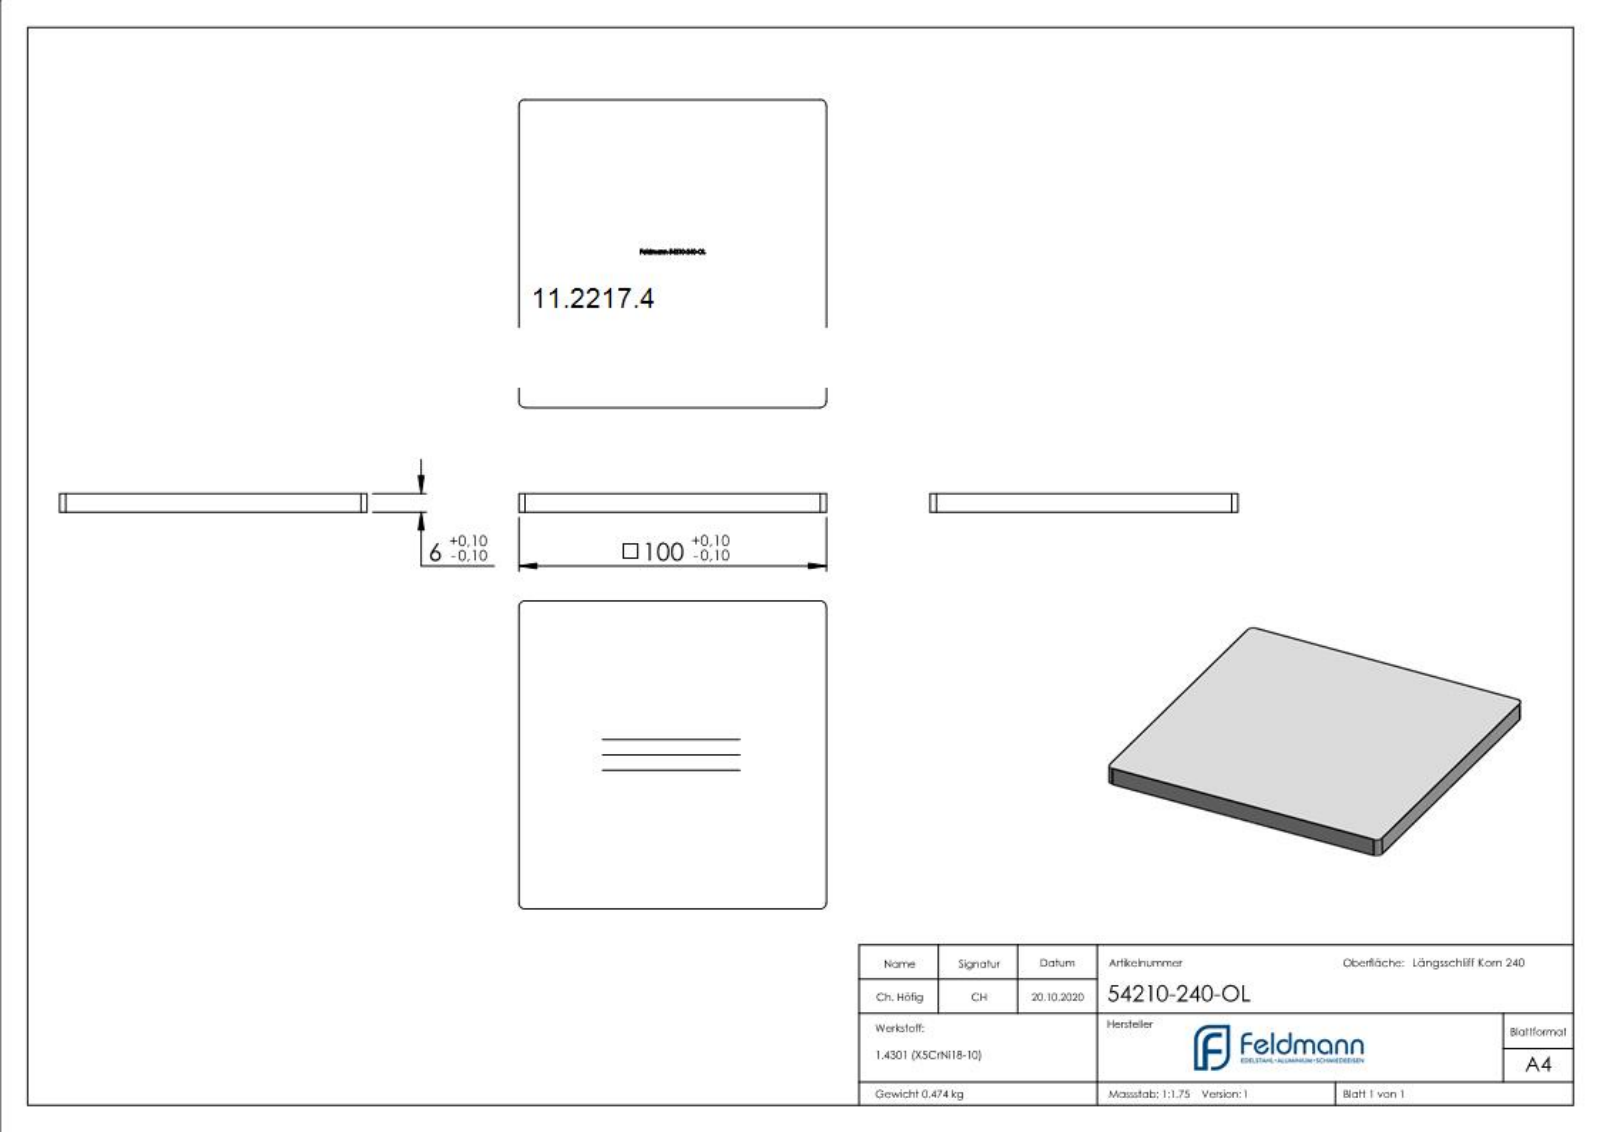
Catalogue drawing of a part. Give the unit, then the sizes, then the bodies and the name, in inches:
Units: inches
Overall size (bounding box): 3.937 × 3.937 × 0.236
Partial cylindrical surfaces — rounded edges, fillets, slot ends (radius × count): R0.079 ×4
Main face-to-face distances: 0.236, 3.937, 0.232, 1.969, 0.017, 0.035, 0.722, 0.08, 0.802, 0.185
Volume: 3.66 in³ · Surface area: 34.69 in²
Bodies: 1 solid, 250 faces (152 planar, 4 cylindrical, 94 other)
Part name (STEP PRODUCT): 54210-240-OL
STEP written by: SolidWorks 2018 (CONFIG_CONTROL_DESIGN)
